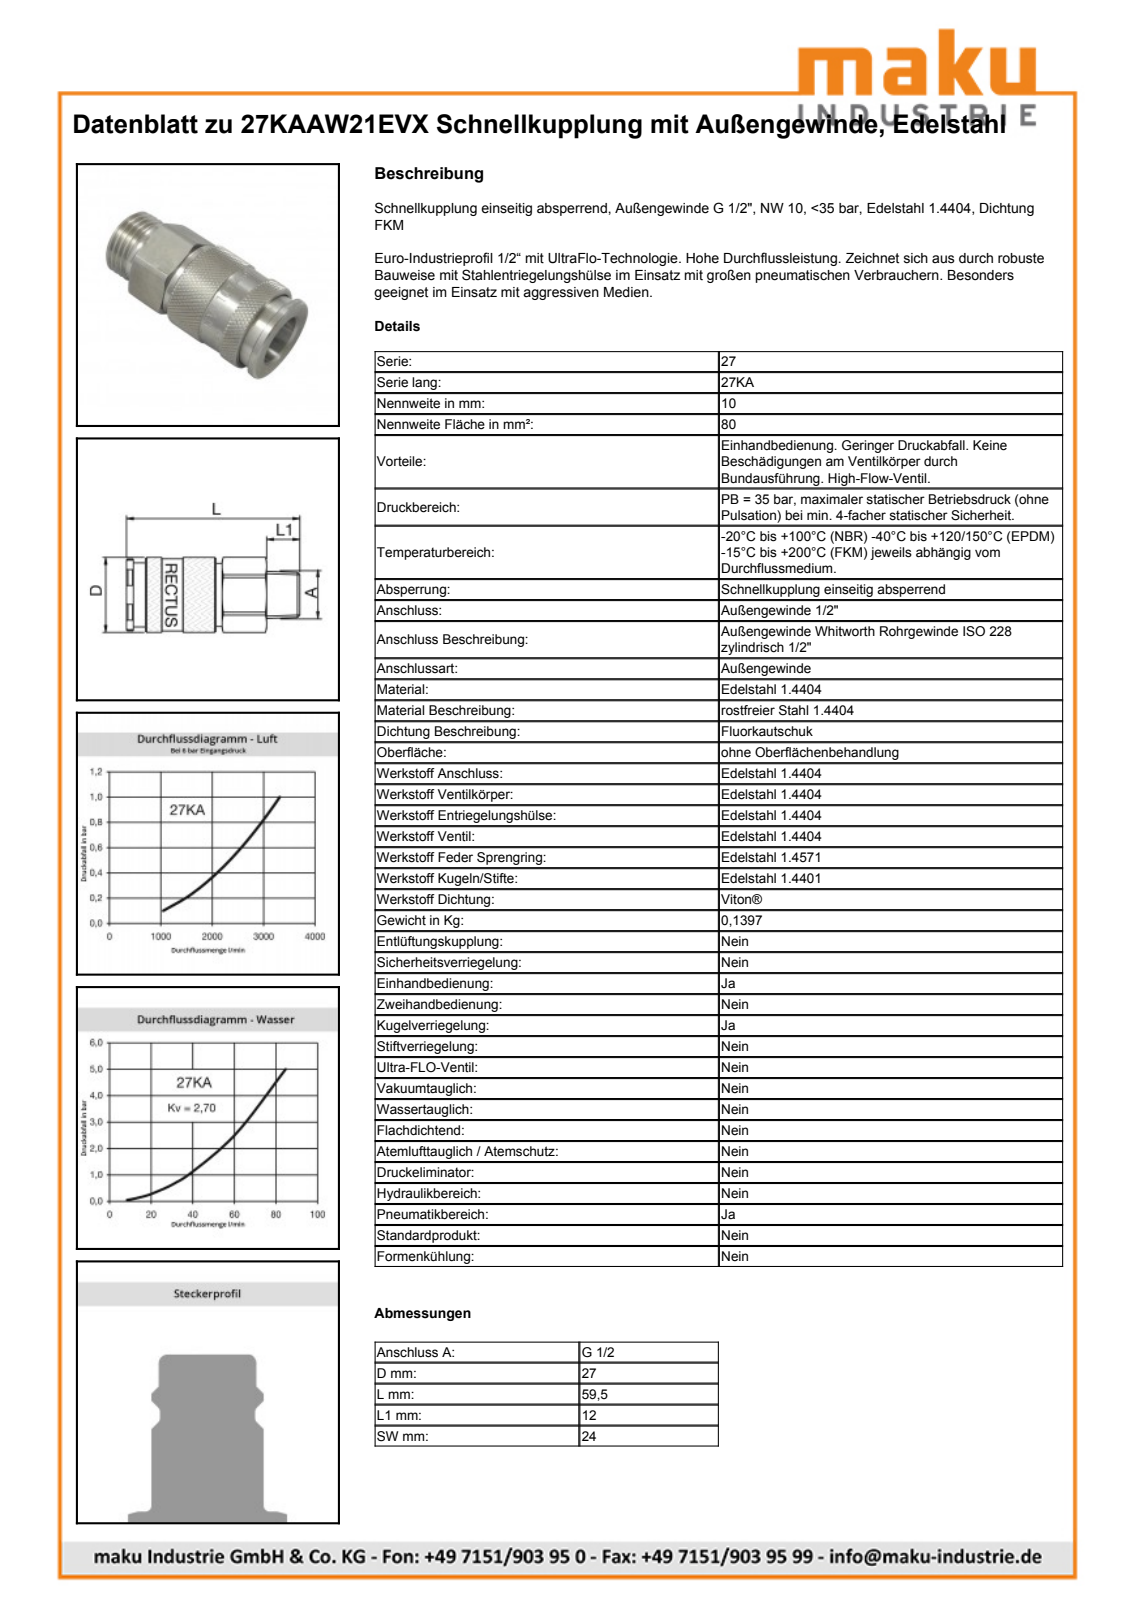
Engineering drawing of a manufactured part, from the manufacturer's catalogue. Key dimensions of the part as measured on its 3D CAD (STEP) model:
Part name (STEP PRODUCT): D104385
STEP written by: Autodesk Inventor 2013 (AUTOMOTIVE_DESIGN)
Units: millimetres
Bodies: 2 solids, 826 faces (323 planar, 87 cylindrical, 416 other)
Overall size (bounding box): 58.75 × 27.15 × 27.15
Volume: 26 261 mm³ · Surface area: 11 926 mm²
Round holes (diameter × count): ⌀17.5 ×1, ⌀18 ×1, ⌀19 ×1, ⌀20.3 ×1, ⌀20.95 ×1, ⌀23.35 ×1, ⌀23.55 ×1
Round bosses / shafts (diameter × count): ⌀27.15 ×1, ⌀26 ×1, ⌀23.1 ×1, ⌀22.8 ×1, ⌀20.95 ×1, ⌀20 ×1, ⌀18.7 ×1, ⌀17.37 ×1
Partial cylindrical surfaces — rounded edges, fillets, slot ends (radius × count): R12.9 ×1, R13.53 ×1
Main face-to-face distances: 23.98, 58.75, 15, 24, 27, 16.75, 31.75, 6.25, 25.5, 52.5
